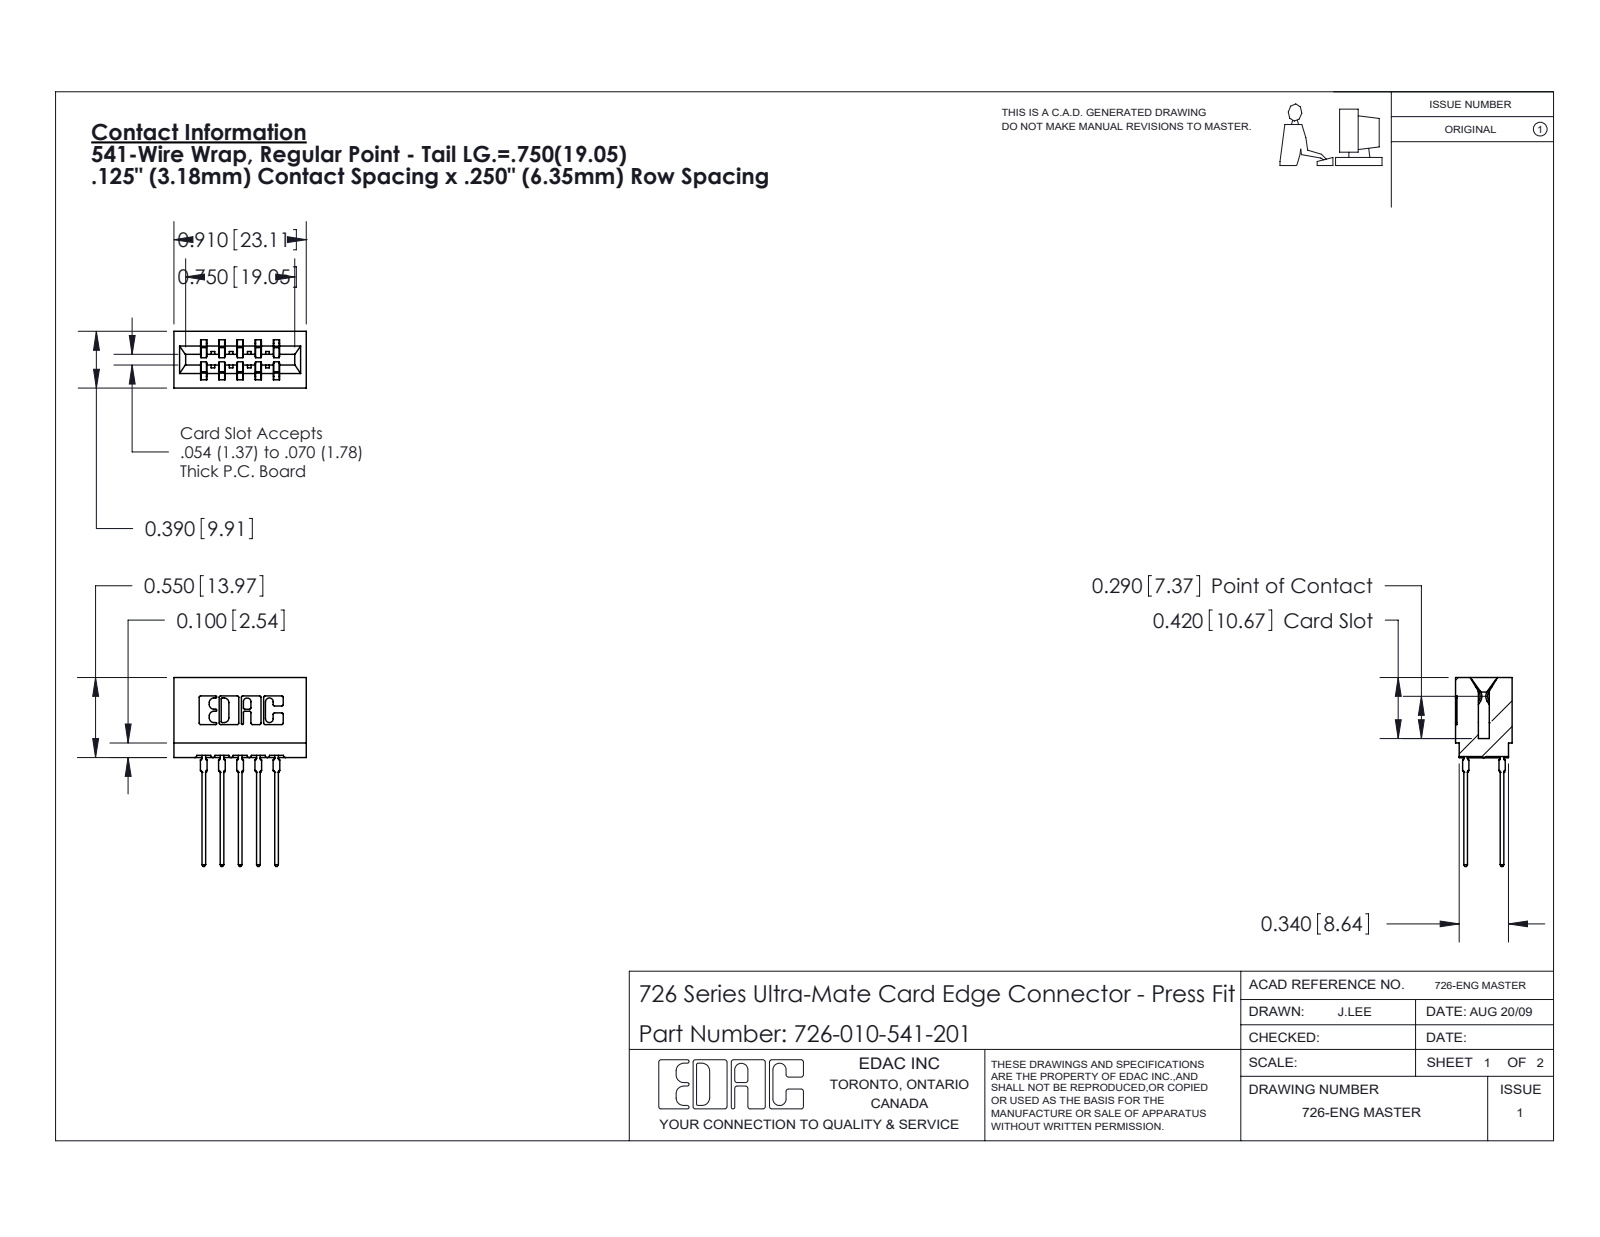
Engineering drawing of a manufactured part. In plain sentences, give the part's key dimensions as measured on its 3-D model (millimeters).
The part is named "726-010-541-201; 746-292-001_541; 726 Part_.515 Slot Depth - 01". Its 3-D file was written by "SolidWorks 2020 (CONFIG_CONTROL_DESIGN)". It is 11 solids with 992 faces: 515 planar, 217 cylindrical and 260 other. Overall it measures 33 by 23.1 by 9.9 millimeters. Its volume is 2 380 cubic millimeters and its surface area 3 561 square millimeters. Partial cylindrical surfaces (rounded edges, fillets, slot ends): 22 of radius 0.3, 20 of radius 0.5, 8 of radius 0.1, 8 of radius 0.3, 6 of radius 0.2, 6 of radius 0.4, 6 of radius 0.8, 3 of radius 0.7. The main face-to-face distances are 6.4, 1.4, 8.5, 0.6, 3.2, 3.2, 1.1, 2.1, 7.8, 9.9.
